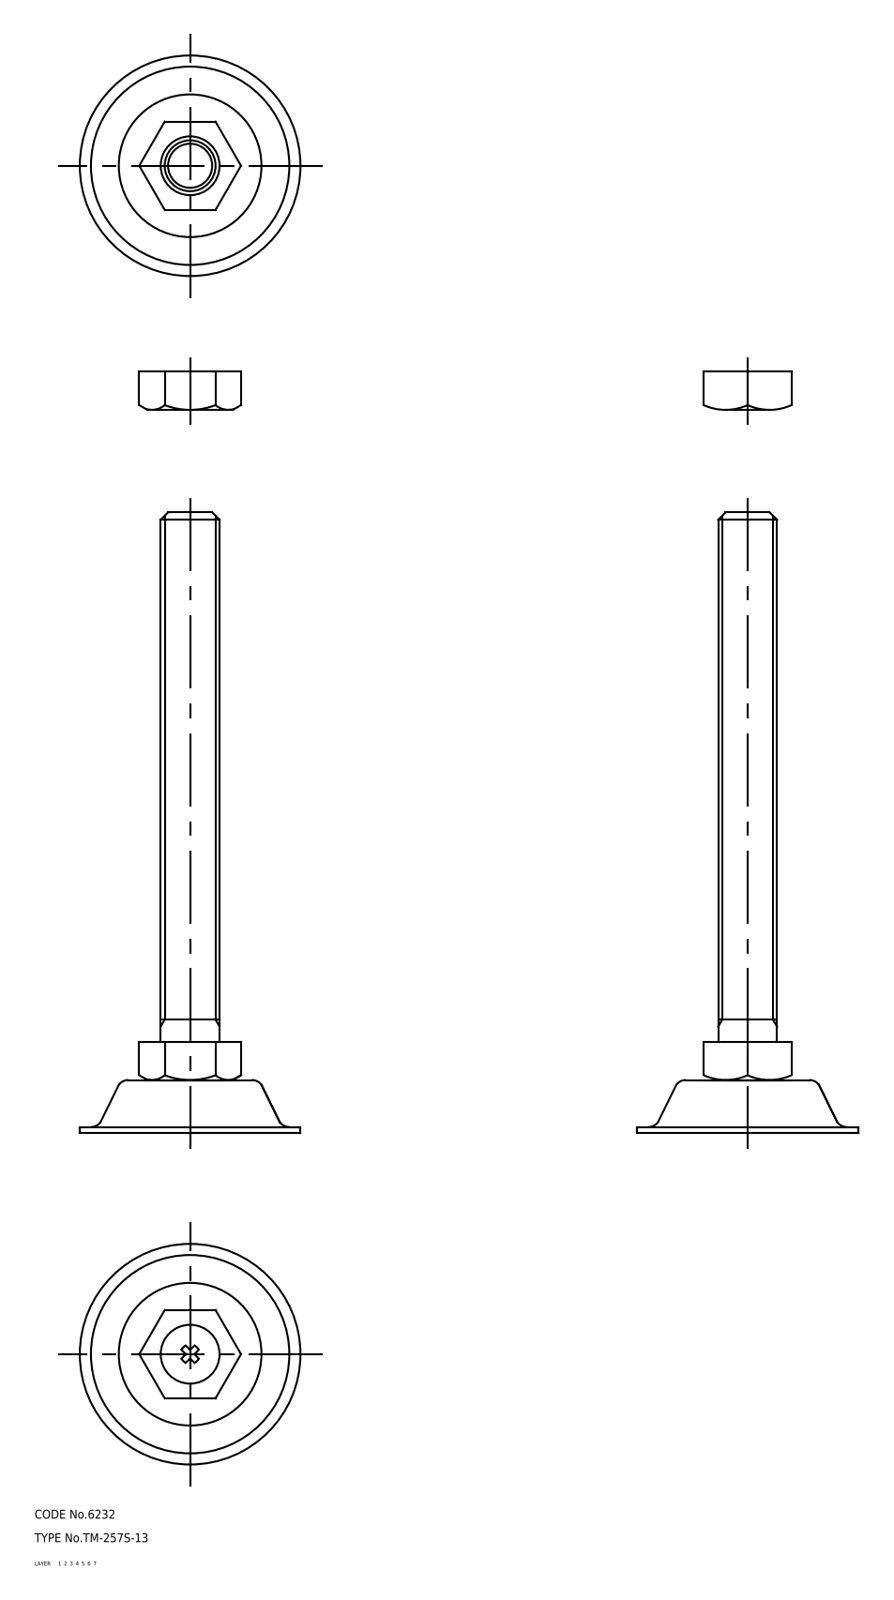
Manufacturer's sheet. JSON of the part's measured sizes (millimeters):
{"part_name": "nut; foot; bolt; TM_257S_13_10194_36", "step_written_by": "CADfix (AUTOMOTIVE_DESIGN)", "units": "millimeters", "bodies": {"solids": 4, "faces": 83, "planar": 0, "cylindrical": 0, "other": 83}, "overall_size": [211, 75, 75], "volume_mm3": 94705, "surface_area_mm2": 33066}
